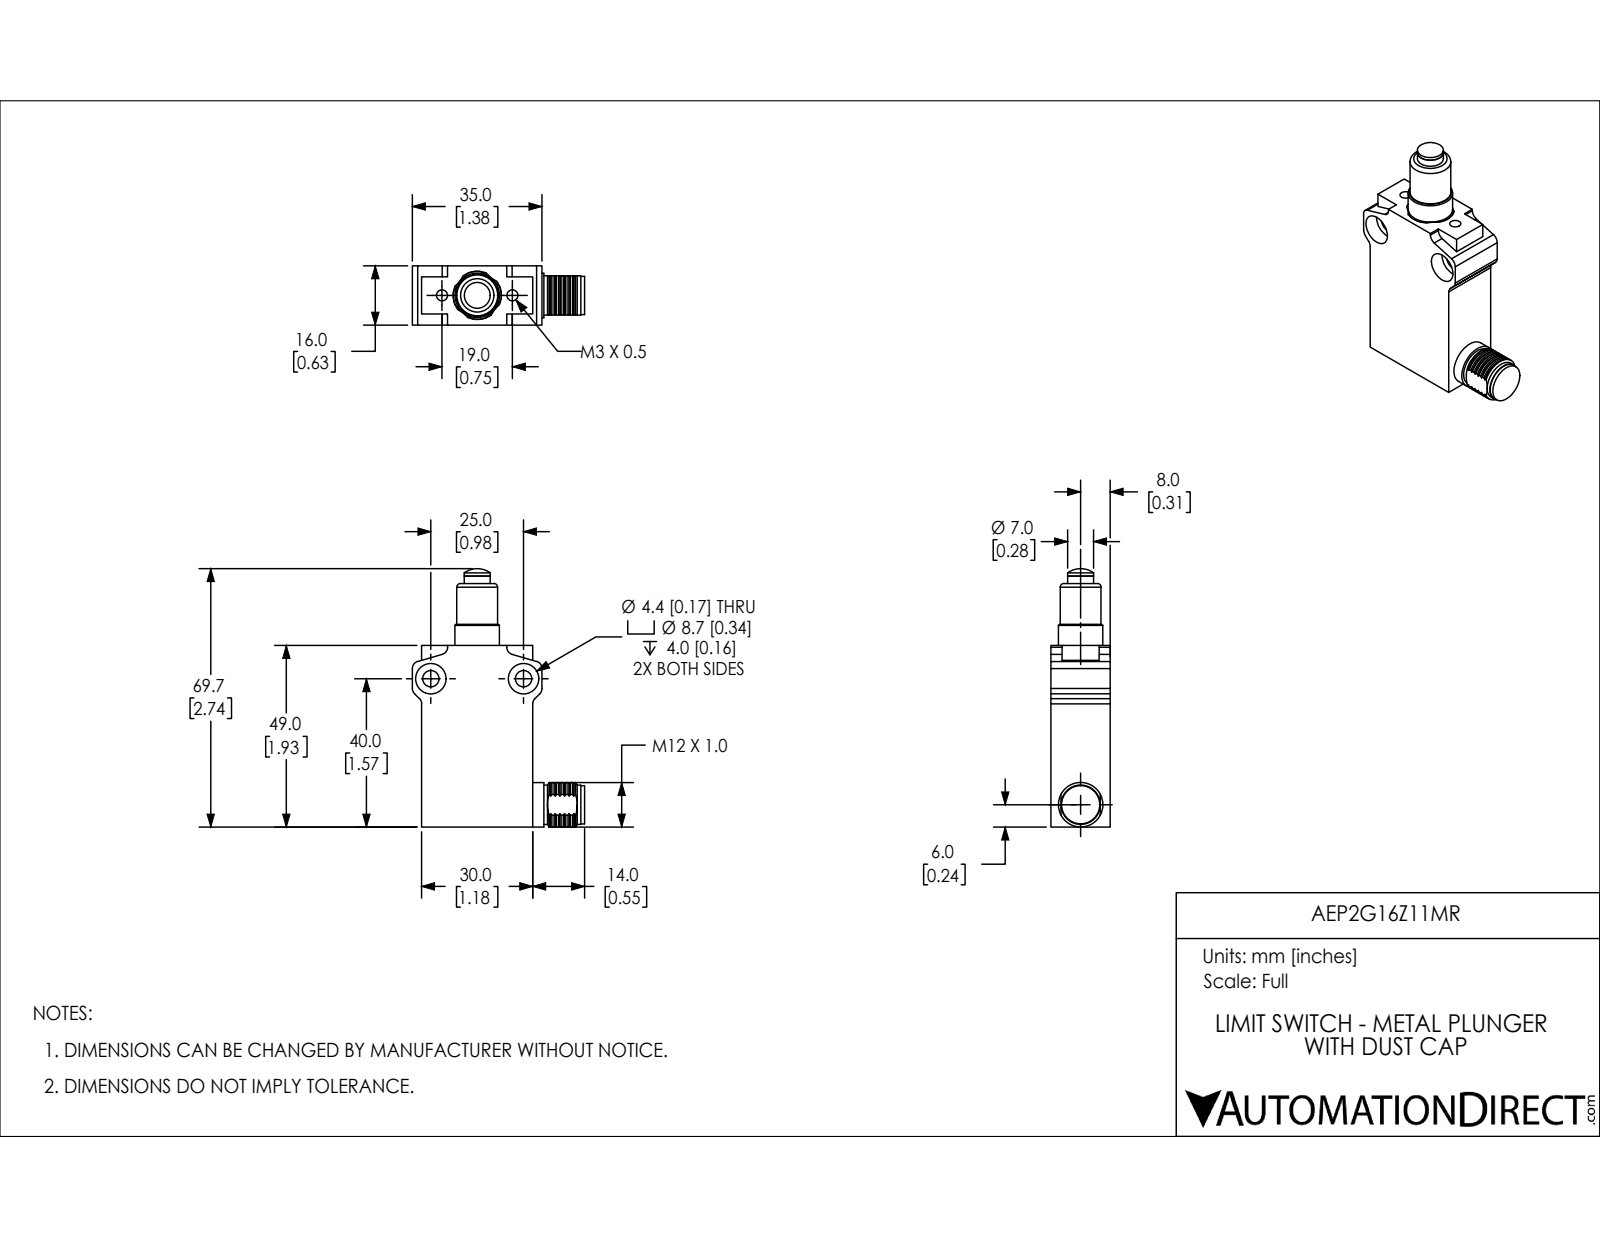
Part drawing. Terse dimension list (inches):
name: AEP2G16Z11MR
written by: SolidWorks 2018 (AUTOMOTIVE_DESIGN)
unit: in
bodies: 4 solids, 202 faces (56 planar, 94 cylindrical, 52 other)
size: 2.744 × 1.831 × 0.63
volume: 1.58 in³; area: 14.43 in²
holes: 2× ⌀0.118, 2× ⌀0.173, 2× ⌀0.323, 1× ⌀0.197, 1× ⌀0.28
bosses: 2× ⌀0.472, 1× ⌀0.433, 1× ⌀0.417, 1× ⌀0.406, 1× ⌀0.276
rounds: 8× R0.079, 1× R0.256
face distances: 0.63, 1.181, 1.929, 0.472, 1.74, 0.189, 0.098, 1.28, 0.157, 0.039
hole spacings: 0.374, 0.748, 0.984
